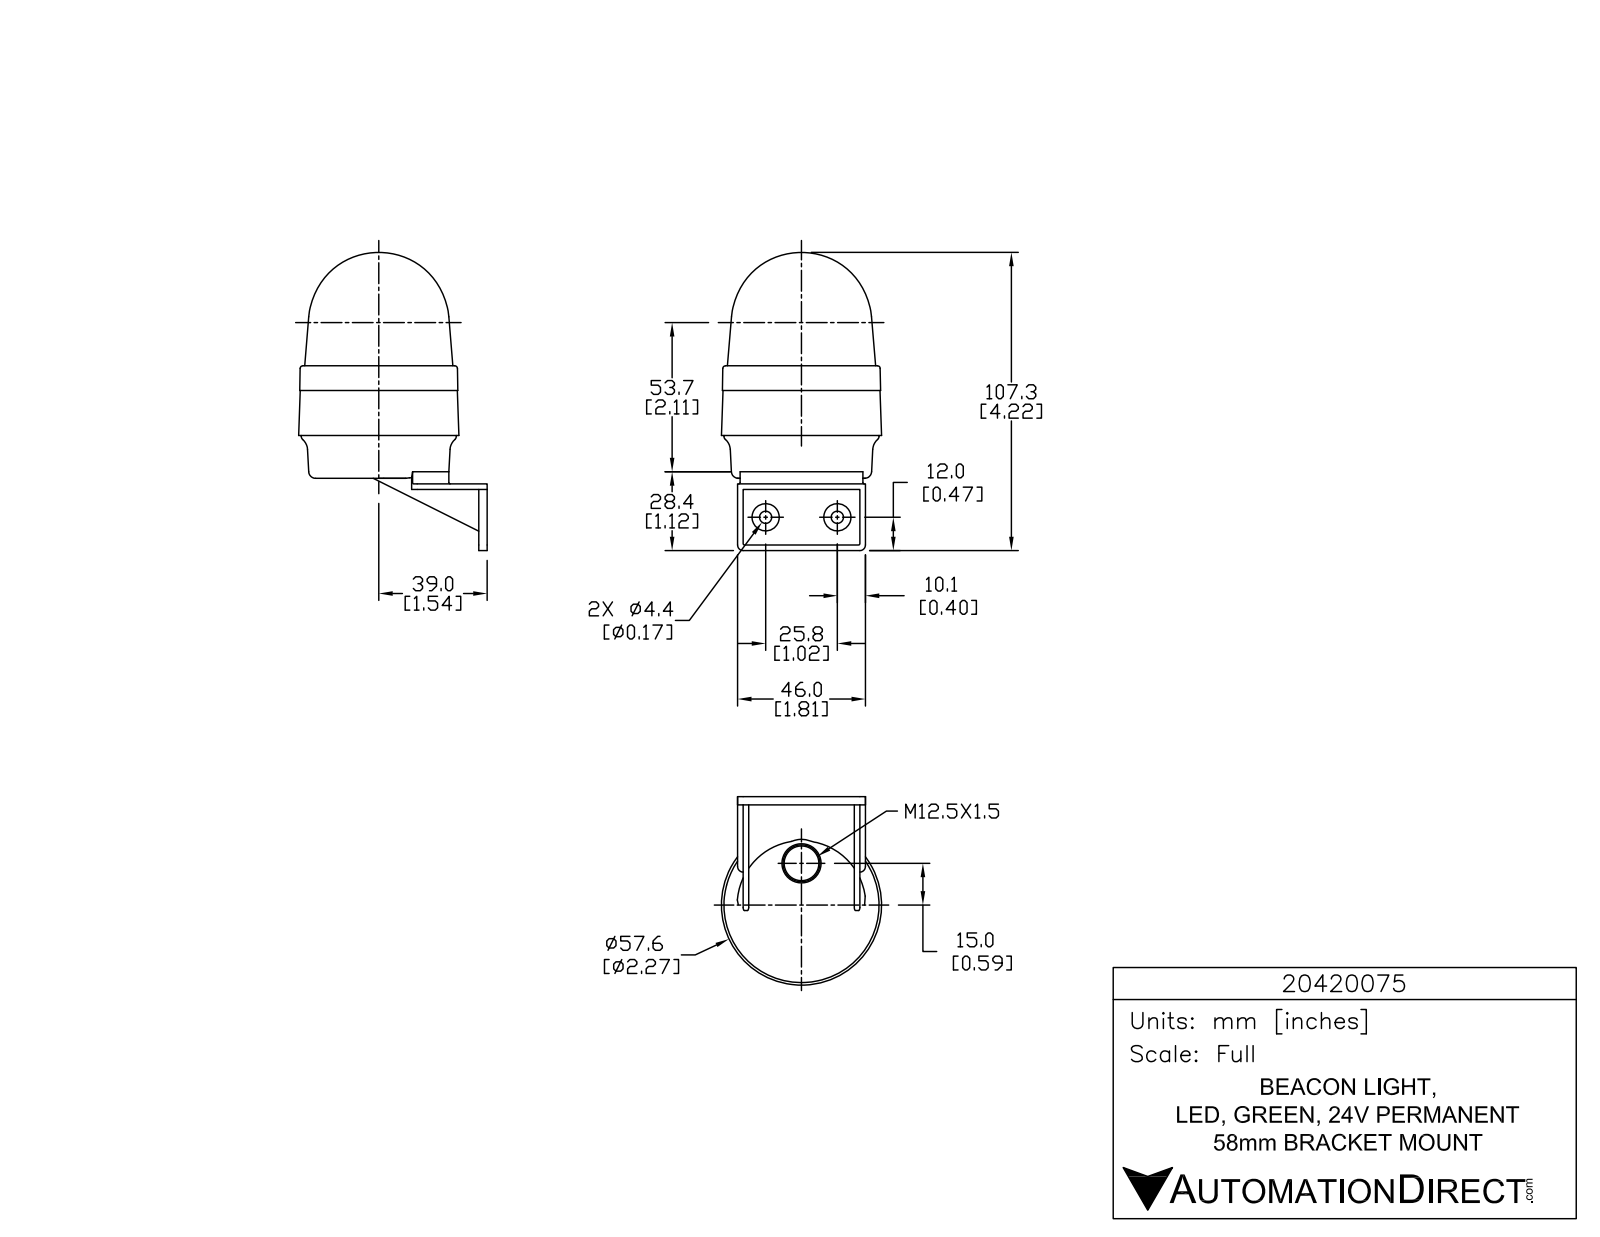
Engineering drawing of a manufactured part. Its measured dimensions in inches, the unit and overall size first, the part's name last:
Units: inches
Overall size (bounding box): 4.225 × 2.852 × 2.407
Round holes (diameter × count): ⌀0.039 ×3, ⌀0.173 ×2
Round bosses / shafts (diameter × count): ⌀0.226 ×3, ⌀0.056 ×3, ⌀0.386 ×2, ⌀2.197 ×1
Partial cylindrical surfaces — rounded edges, fillets, slot ends (radius × count): R0.008 ×6, R0.008 ×6, R0.008 ×6, R0.02 ×6, R0.131 ×6, R0.079 ×4, R0.004 ×3, R0.005 ×3
Main face-to-face distances: 0.079, 0.157, 1.575, 1.654, 0.039, 0.118, 1.496, 0.866, 0.945, 0.764
Hole centre spacings: 1.016
Volume: 10.27 in³ · Surface area: 33.38 in²
Bodies: 1 solid, 828 faces (551 planar, 179 cylindrical, 98 other)
Part name (STEP PRODUCT): 20420075
STEP written by: SolidWorks 2015 (AUTOMOTIVE_DESIGN)
